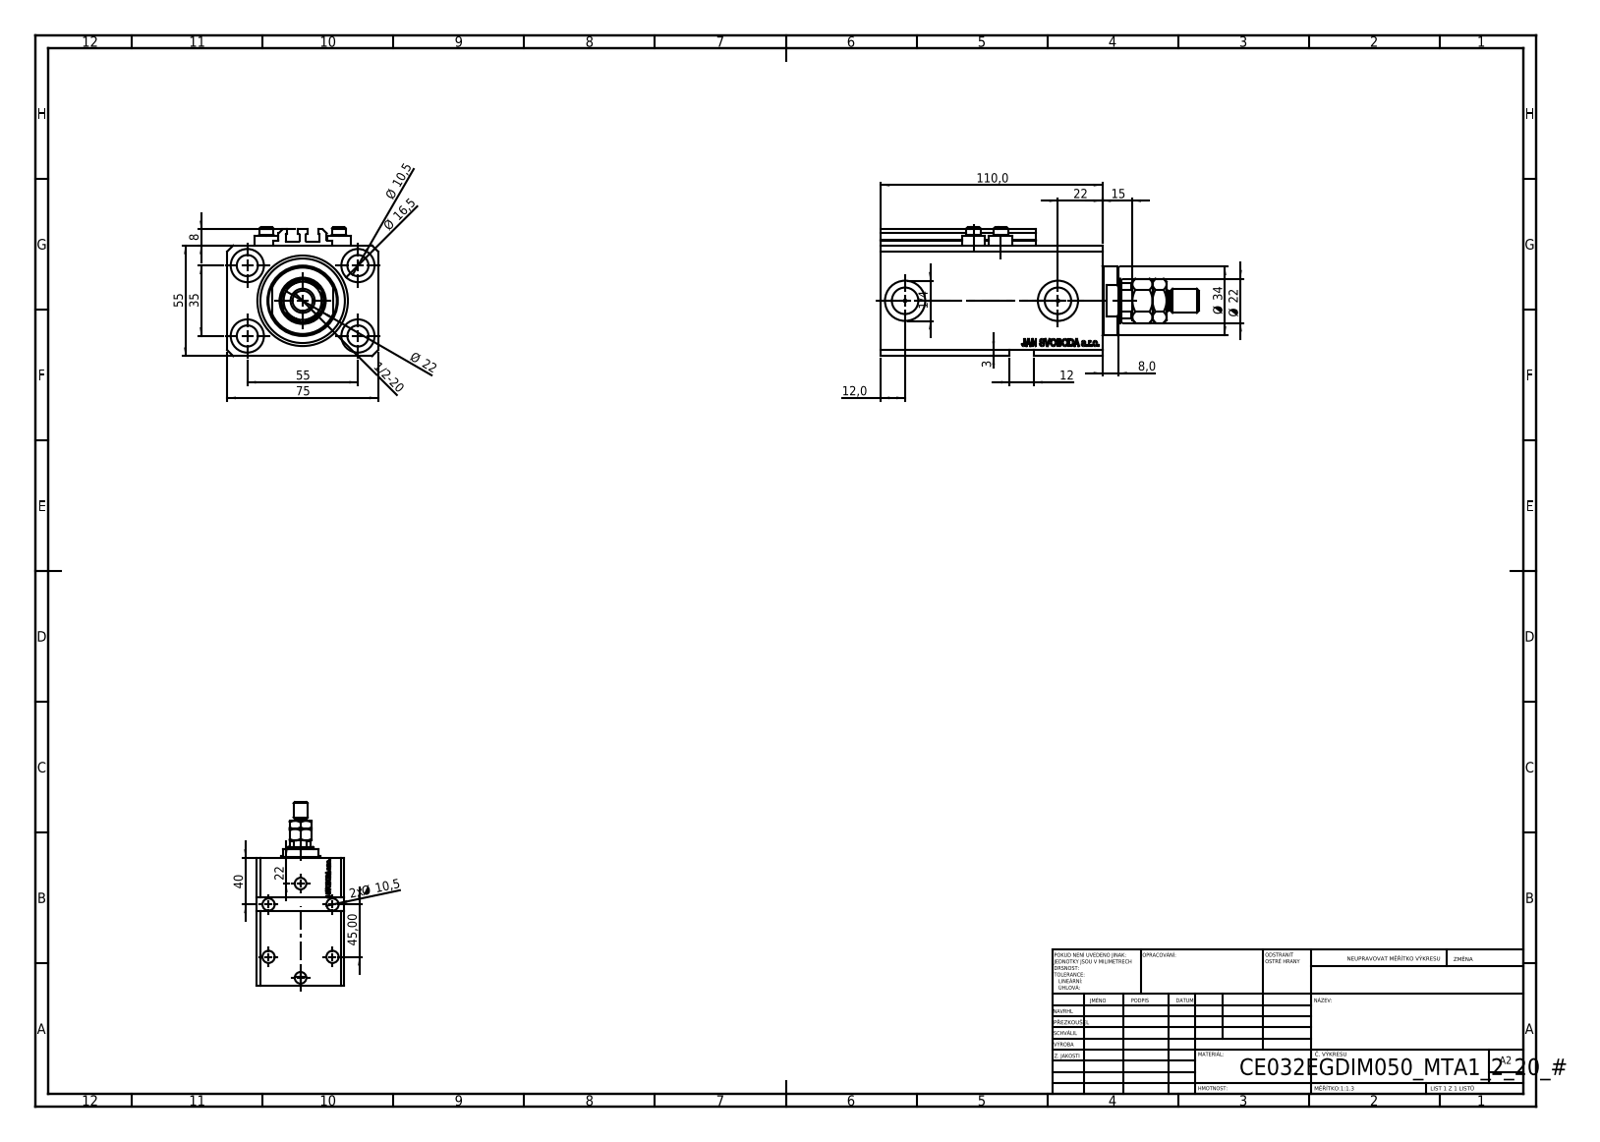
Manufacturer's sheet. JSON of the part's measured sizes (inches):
{"part_name": "ALLEN BOLT V250CE; MTA; V250CE_E_Body; V250CE_C_VCP (+1 more)", "step_written_by": "SolidWorks 2019 (CONFIG_CONTROL_DESIGN)", "units": "inches", "bodies": {"solids": 9, "faces": 1149, "planar": 533, "cylindrical": 162, "other": 454}, "overall_size": [6.22, 2.953, 2.52], "volume_in3": 23.48, "surface_area_in2": 153.6, "round_holes": [[0.413, 9], [0.049, 4], [0.157, 4], [0.65, 4], [0.394, 2], [0.518, 2], [0.787, 2], [0.866, 1], [1.26, 1], [1.772, 1]], "round_bosses_or_shafts": [[0.457, 4], [0.276, 4], [1.339, 1], [0.472, 1], [0.394, 1]], "partial_cylinders_radius": [[0.008, 10], [0.413, 1]], "face_to_face_distances": [2.165, 2.953, 0.591, 4.331, 3.74, 0.39, 0.118, 3.35, 3.941, 0.098], "hole_center_spacings": [1.283, 1.294, 2.165, 2.706, 0.535, 0.555, 0.907, 1.016]}
